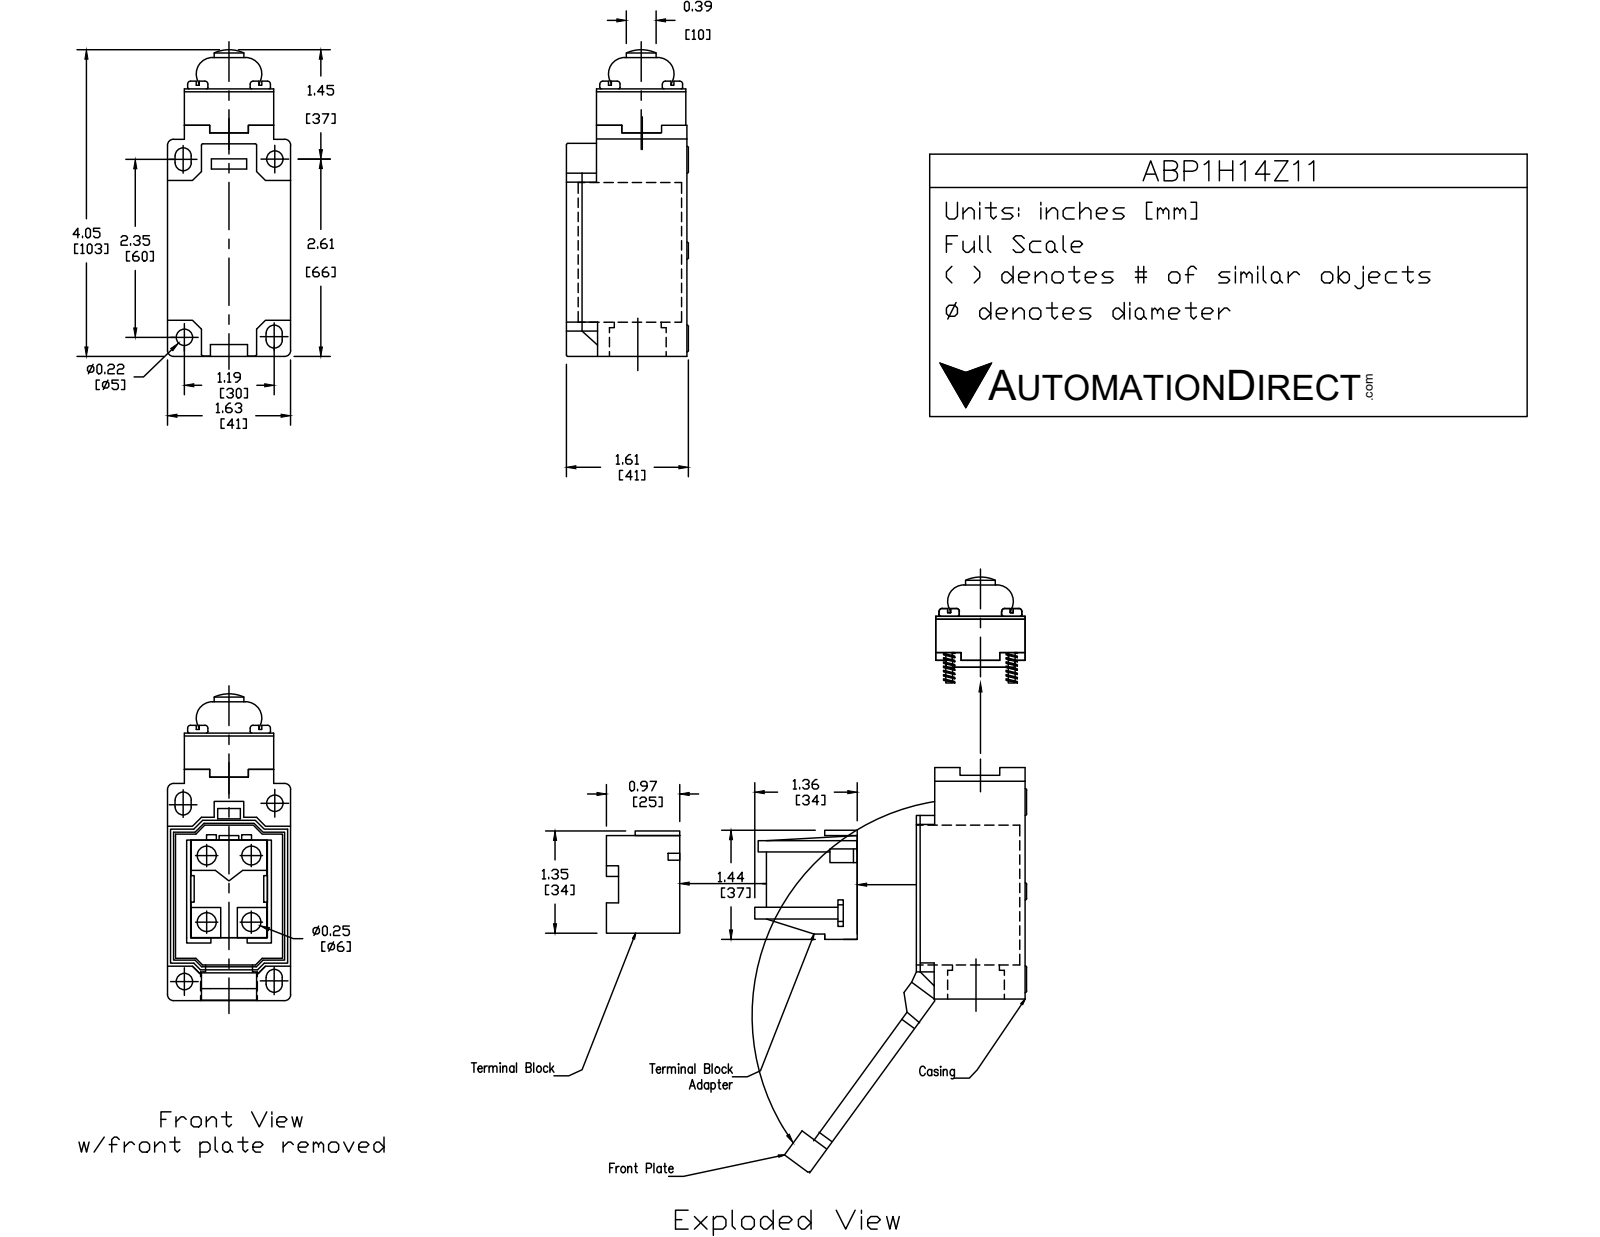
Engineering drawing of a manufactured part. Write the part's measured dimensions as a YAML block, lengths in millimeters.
part_name: "ABP1H14Z11"
step_written_by: "SolidWorks 2017 (AUTOMOTIVE_DESIGN)"
units: millimeters
bodies: {solids: 3, faces: 173, planar: 77, cylindrical: 74, other: 22}
overall_size: [103.4, 41, 40.3]
volume: 126500
surface_area: 24260
round_holes:
  - {diameter: 5.4, count: 2}
  - {diameter: 10.1, count: 1}
  - {diameter: 17, count: 1}
  - {diameter: 19, count: 1}
  - {diameter: 20.5, count: 1}
round_bosses_or_shafts:
  - {diameter: 9, count: 4}
  - {diameter: 7, count: 4}
  - {diameter: 20, count: 1}
  - {diameter: 10, count: 1}
partial_cylinders:
  - {radius: 0.5, count: 16}
  - {radius: 0.6, count: 4}
  - {radius: 2, count: 4}
  - {radius: 2.7, count: 4}
  - {radius: 11.5, count: 1}
  - {radius: 12, count: 1}
face_to_face_distances: [41, 39.8, 30, 75.5, 9.8, 5.5, 35.5, 78, 2.5, 12]
hole_center_spacings: [1.5, 67.1]
